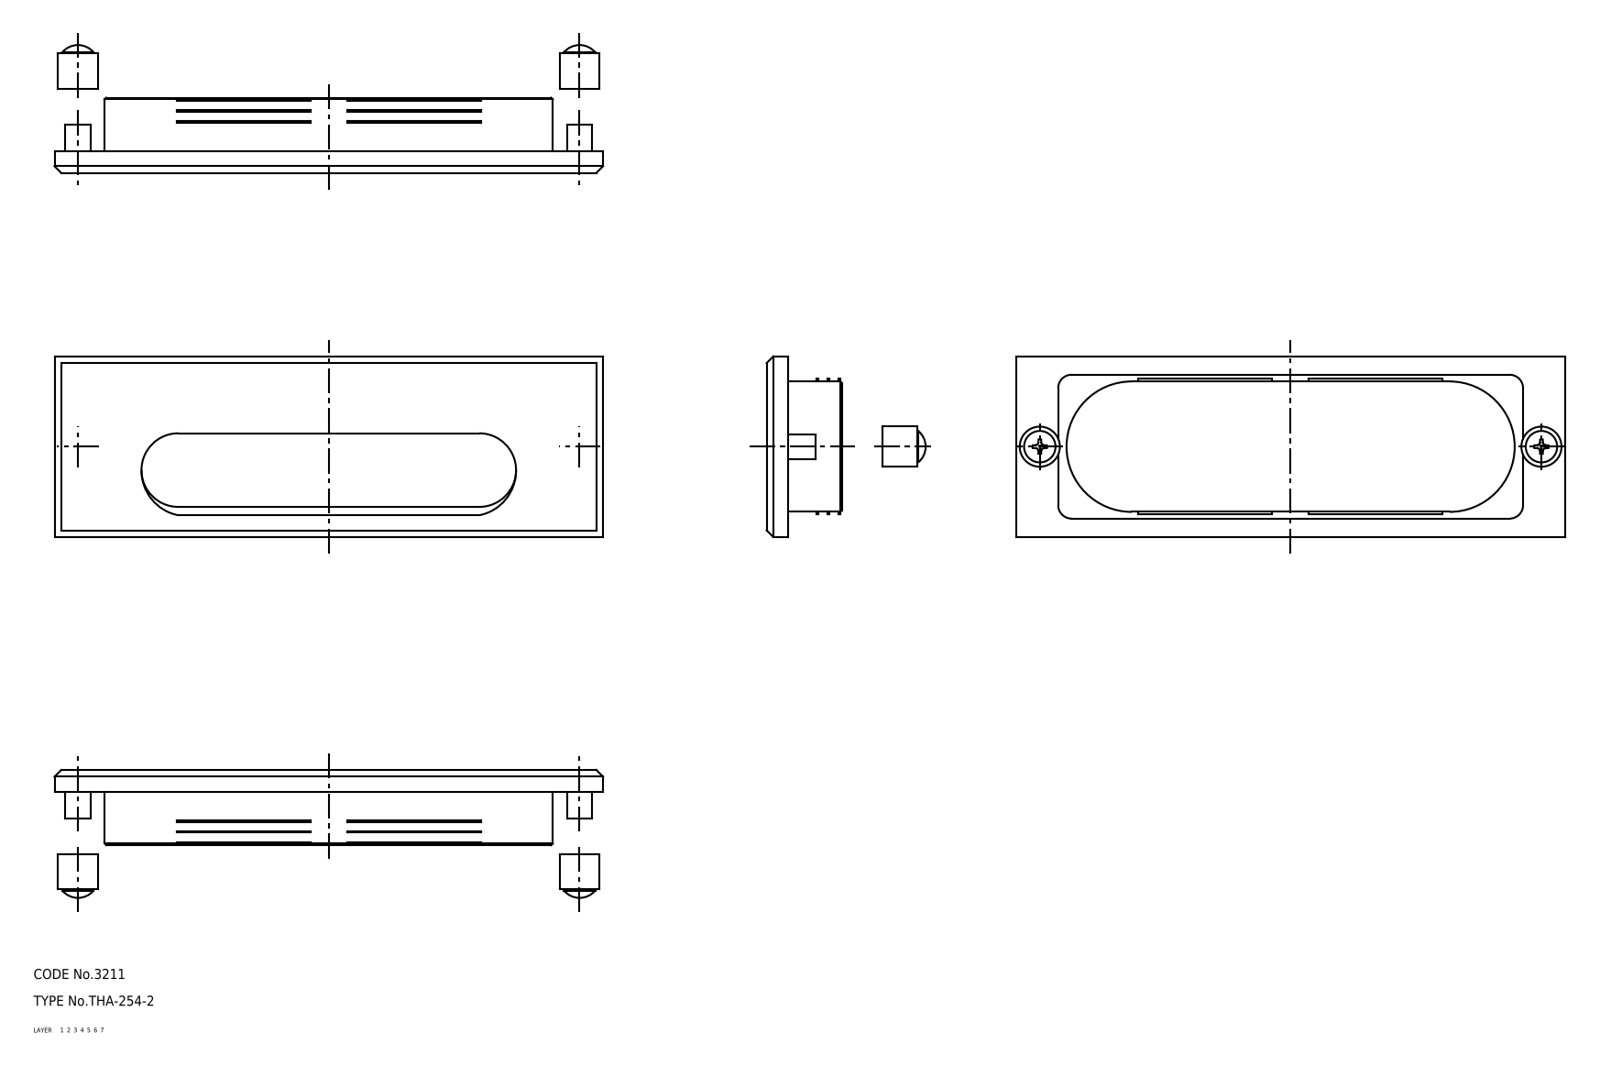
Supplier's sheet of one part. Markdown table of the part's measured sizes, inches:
| quantity | value |
| --- | --- |
| part name | spacer; screw; cover; base (+1 more) |
| STEP written by | CADfix (AUTOMOTIVE_DESIGN) |
| units | inches |
| bodies | 6 solids, 195 faces (0 planar, 0 cylindrical, 195 other) |
| overall size | 6.457 × 2.126 × 0.886 |
| volume | 3.081 in³ |
| surface area | 65.74 in² |
